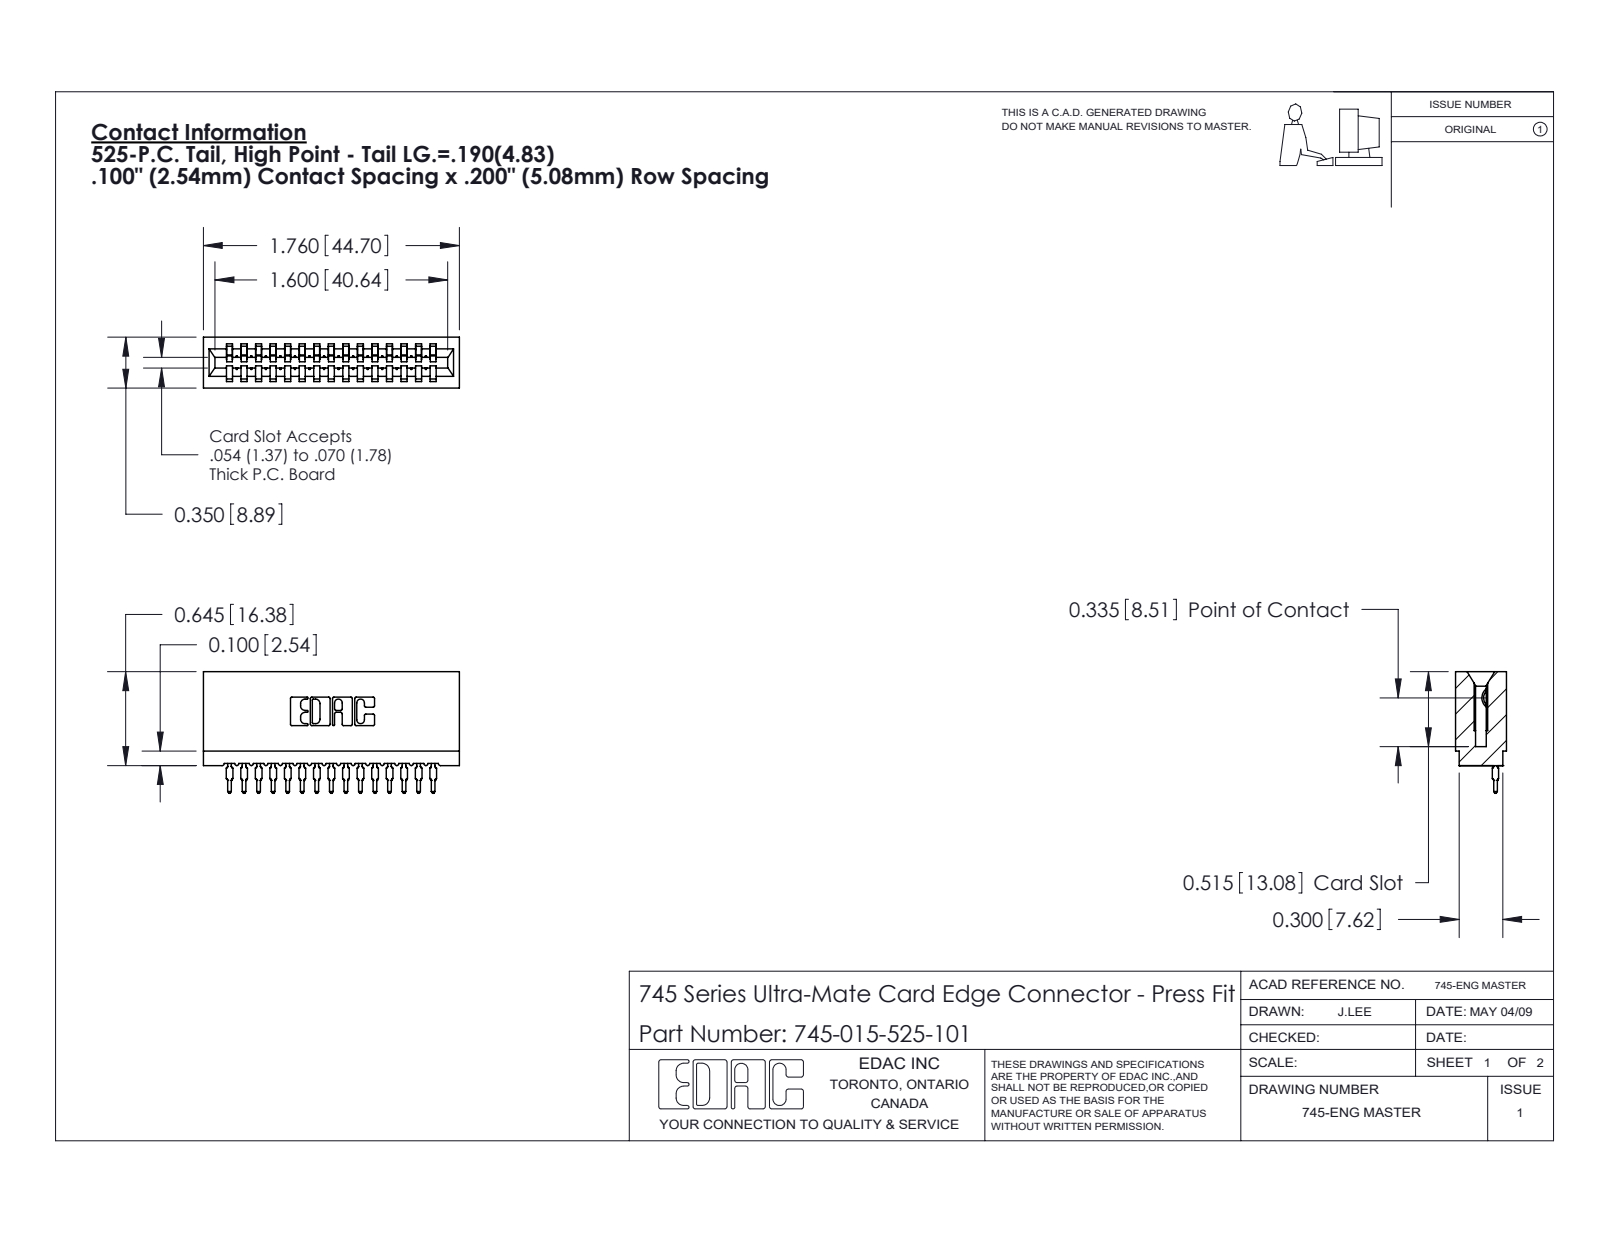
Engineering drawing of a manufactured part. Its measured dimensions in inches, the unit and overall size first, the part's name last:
Units: inches
Overall size (bounding box): 1.76 × 0.836 × 0.35
Partial cylindrical surfaces — rounded edges, fillets, slot ends (radius × count): R0.015 ×30, R0.021 ×30, R0.01 ×22, R0.007 ×6, R0.031 ×6, R0.005 ×4, R0.011 ×4, R0.026 ×3
Main face-to-face distances: 0.1, 0.2, 0.3, 0.4, 0.35, 0.5, 0.6, 0.7, 0.138, 0.212
Volume: 0.246 in³ · Surface area: 10.79 in²
Bodies: 16 solids, 1775 faces (1060 planar, 325 cylindrical, 390 other)
Part name (STEP PRODUCT): 745-292-001_525; 745 Part_Insulator Option - 01; 745-015-525-101
STEP written by: SolidWorks 2020 (CONFIG_CONTROL_DESIGN)
